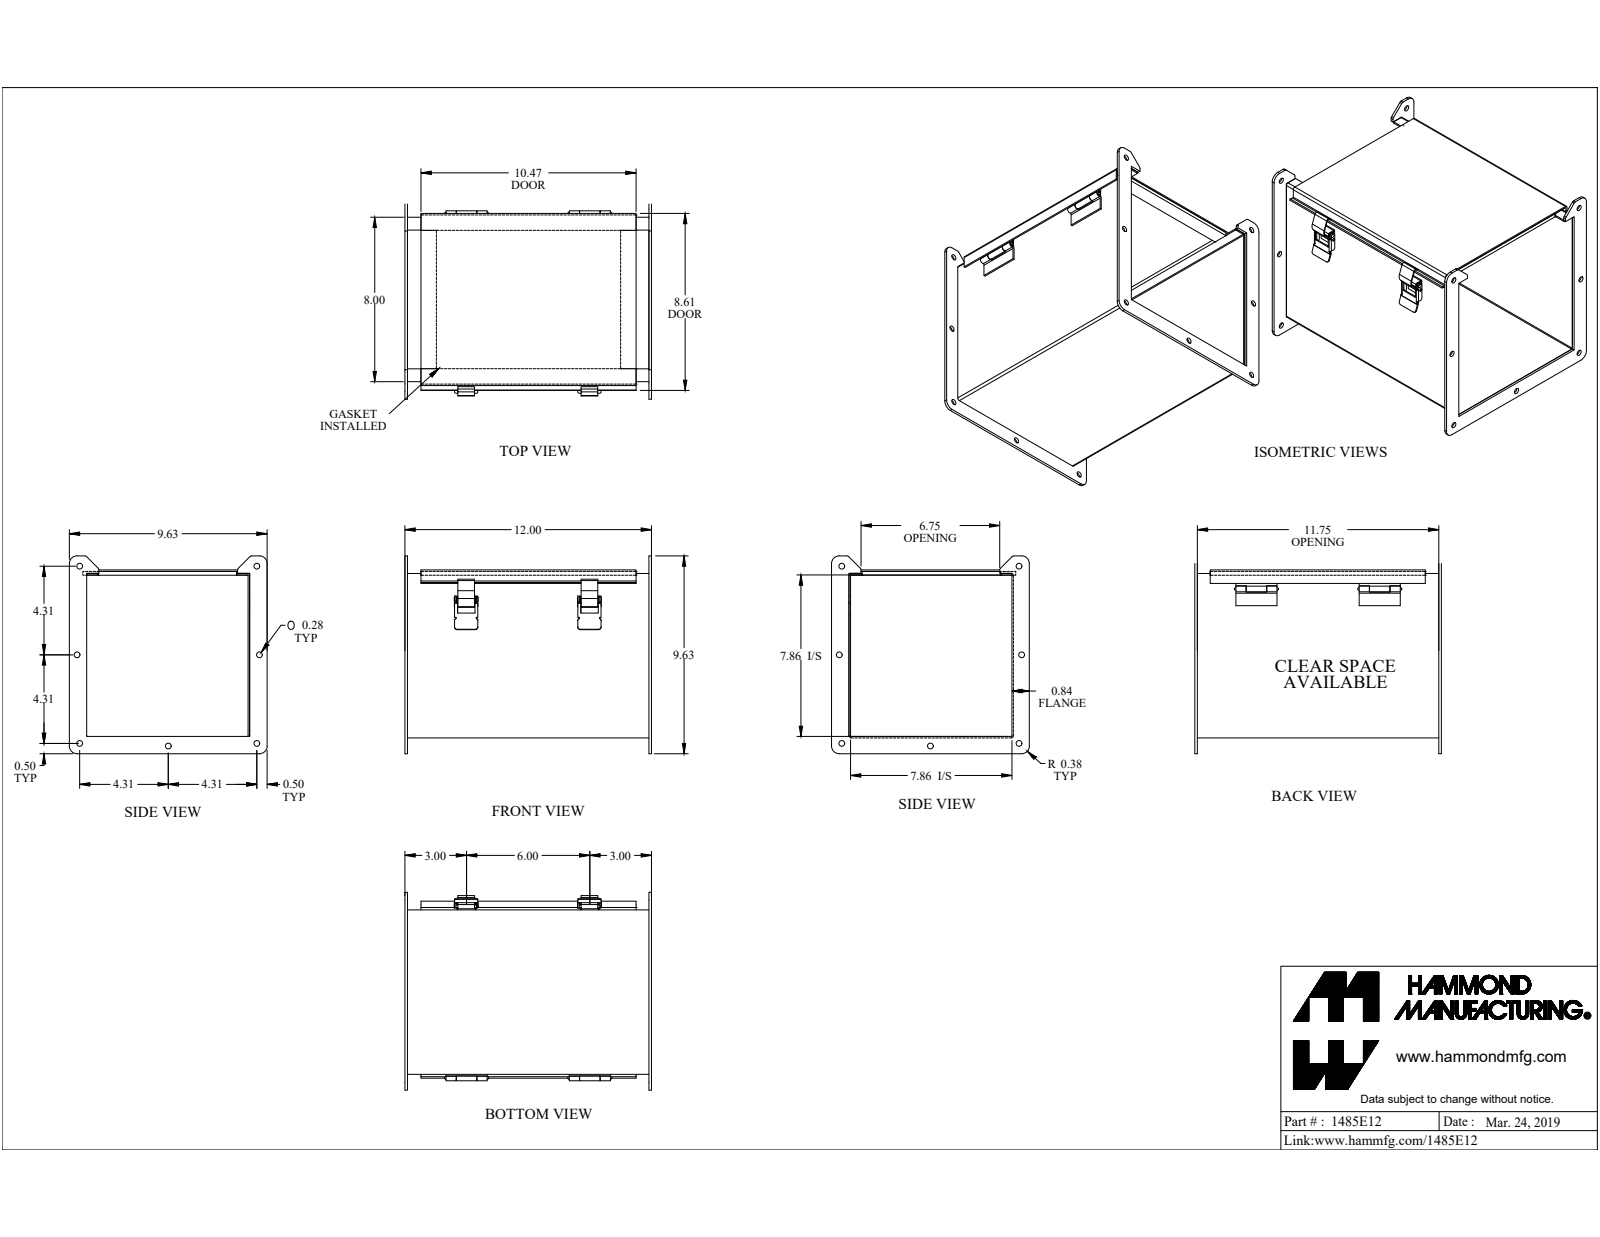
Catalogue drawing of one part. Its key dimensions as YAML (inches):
part_name: "1485E12"
step_written_by: "SolidWorks 2019 (CONFIG_CONTROL_DESIGN)"
units: inches
bodies: {solids: 20, faces: 416, planar: 250, cylindrical: 162, other: 4}
overall_size: [12, 9.625, 9.625]
volume: 40.02
surface_area: 1008
round_holes:
  - {diameter: 0.281, count: 7}
  - {diameter: 0.125, count: 1}
  - {diameter: 0.13, count: 1}
  - {diameter: 0.164, count: 1}
round_bosses_or_shafts:
  - {diameter: 0.187, count: 2}
  - {diameter: 0.275, count: 1}
  - {diameter: 0.156, count: 1}
  - {diameter: 0.125, count: 1}
  - {diameter: 0.125, count: 1}
partial_cylinders:
  - {radius: 0.016, count: 13}
  - {radius: 0.125, count: 9}
  - {radius: 0.036, count: 7}
  - {radius: 0.108, count: 7}
  - {radius: 0.035, count: 5}
  - {radius: 0.039, count: 5}
  - {radius: 0.076, count: 5}
  - {radius: 0.015, count: 4}
face_to_face_distances: [0.072, 7.928, 8.1, 8, 7.856, 8.028, 8.172, 0.125, 11.875, 7.913]
hole_center_spacings: [8.625, 4.314, 4.315, 9.755, 9.755, 6.276, 12.197, 0.285]
